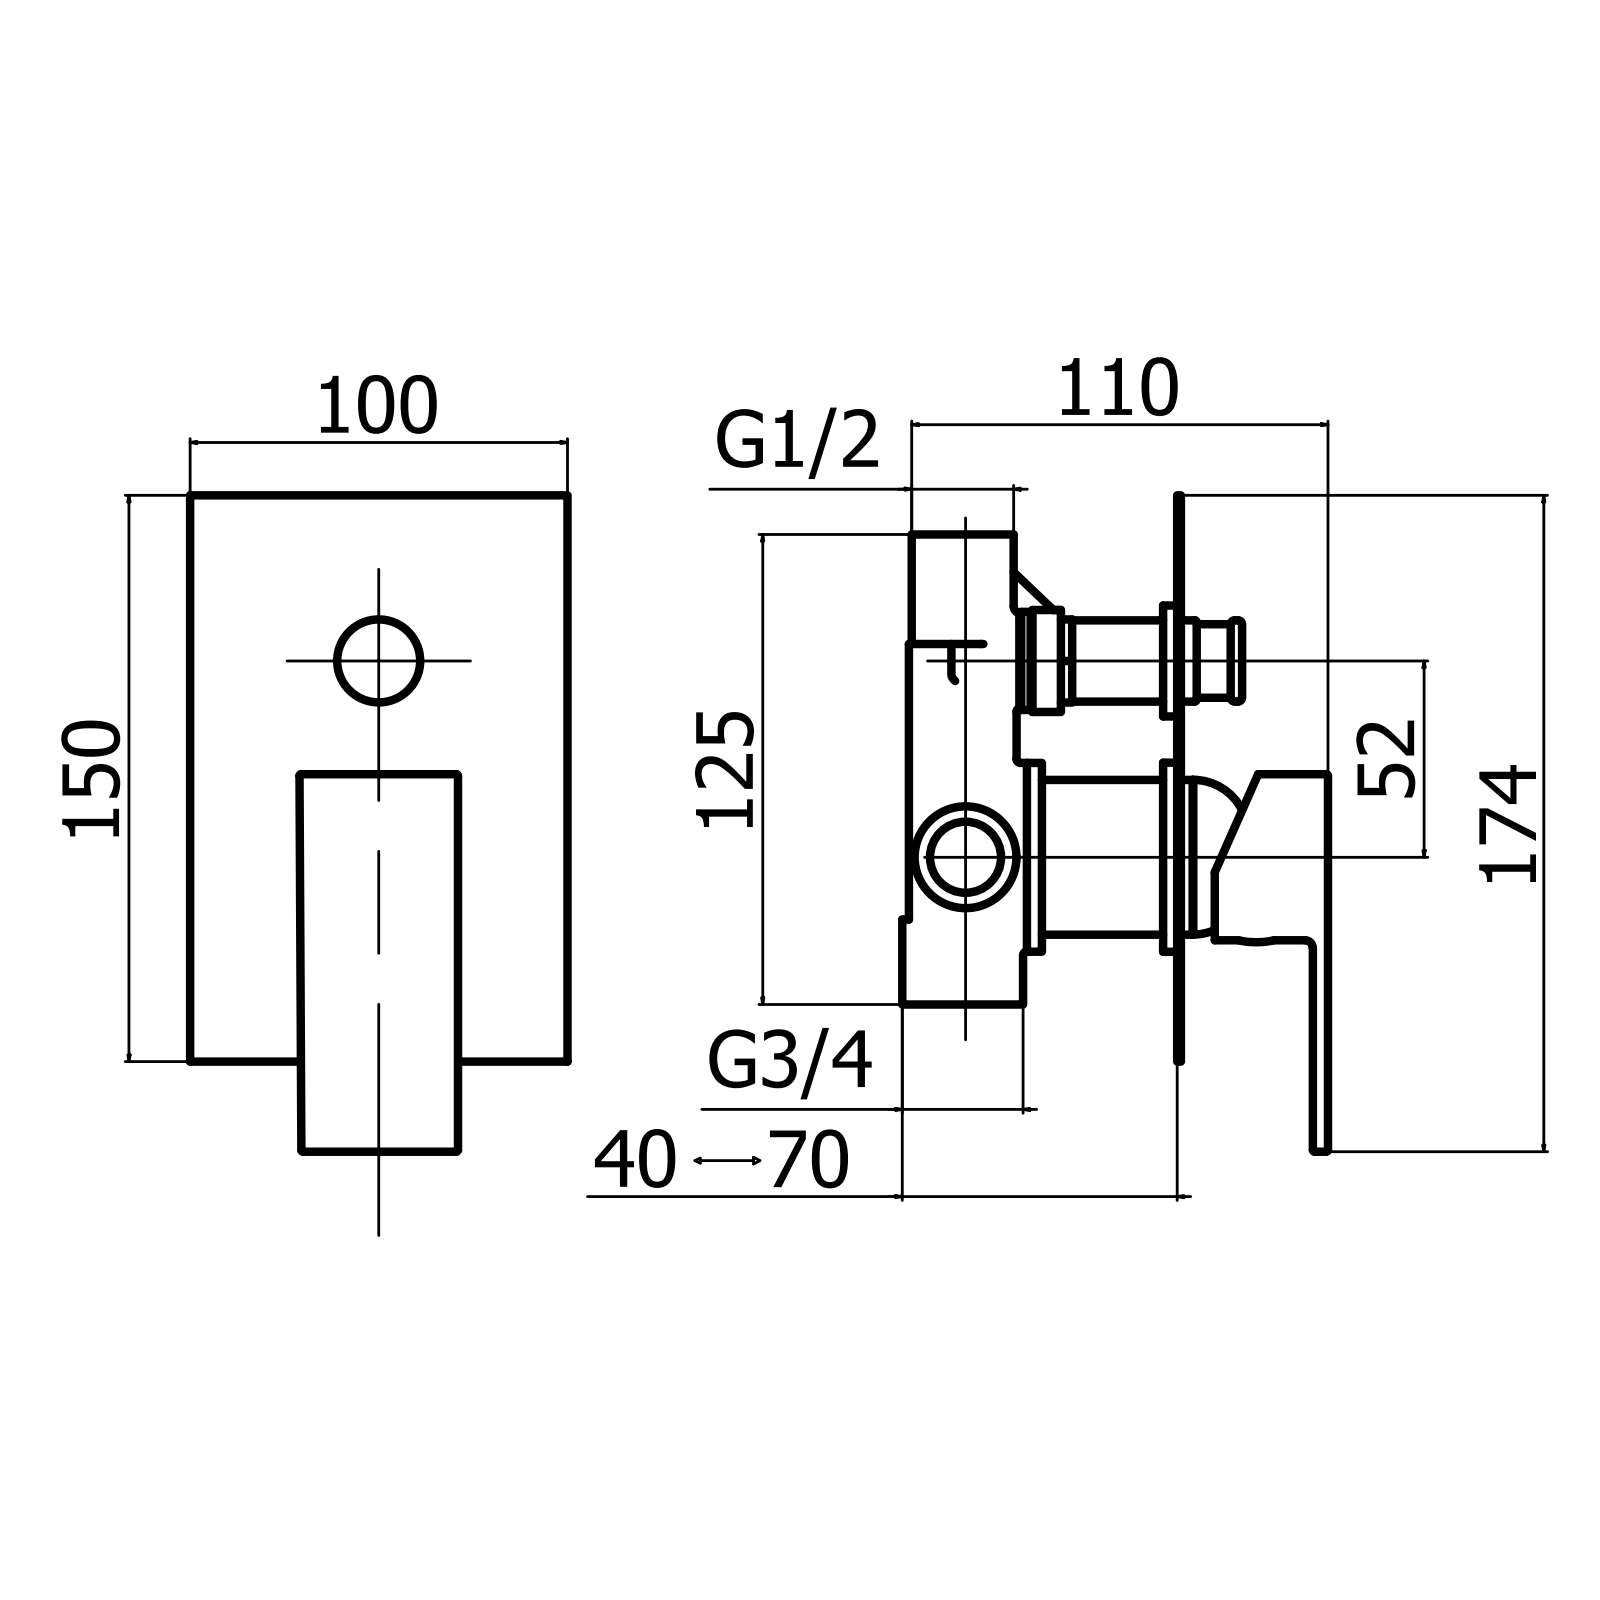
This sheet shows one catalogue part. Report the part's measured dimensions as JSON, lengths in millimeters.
{"part_name": "SINMAC0008; SCCMAC0005; AQDR005C001; SPLMAC0003 (+8 more)", "step_written_by": "CREO PARAMETRIC BY PTC INC, 2020281 (CONFIG_CONTROL_DESIGN)", "units": "millimeters", "bodies": {"solids": 10, "faces": 247, "planar": 57, "cylindrical": 94, "other": 96}, "overall_size": [197.5, 100, 73], "volume_mm3": 101254, "surface_area_mm2": 67438, "round_holes": [[4.2, 1], [4.5, 1], [5, 1], [5.2, 1], [7.5, 1], [9.95, 1], [12, 1], [14, 1], [15, 1], [17.5, 1], [18, 1], [21.5, 1]], "round_bosses_or_shafts": [[49, 1], [42, 1], [34, 1], [27.5, 1], [20.5, 1], [16, 1], [7, 1], [1, 1]], "partial_cylinders_radius": [[0.5, 20], [0.2, 5], [2.6, 1]], "face_to_face_distances": [2, 62.1, 60.1, 57.6, 55.6, 4.5, 41, 30.1, 6, 32.1], "hole_center_spacings": [7.6, 68]}
